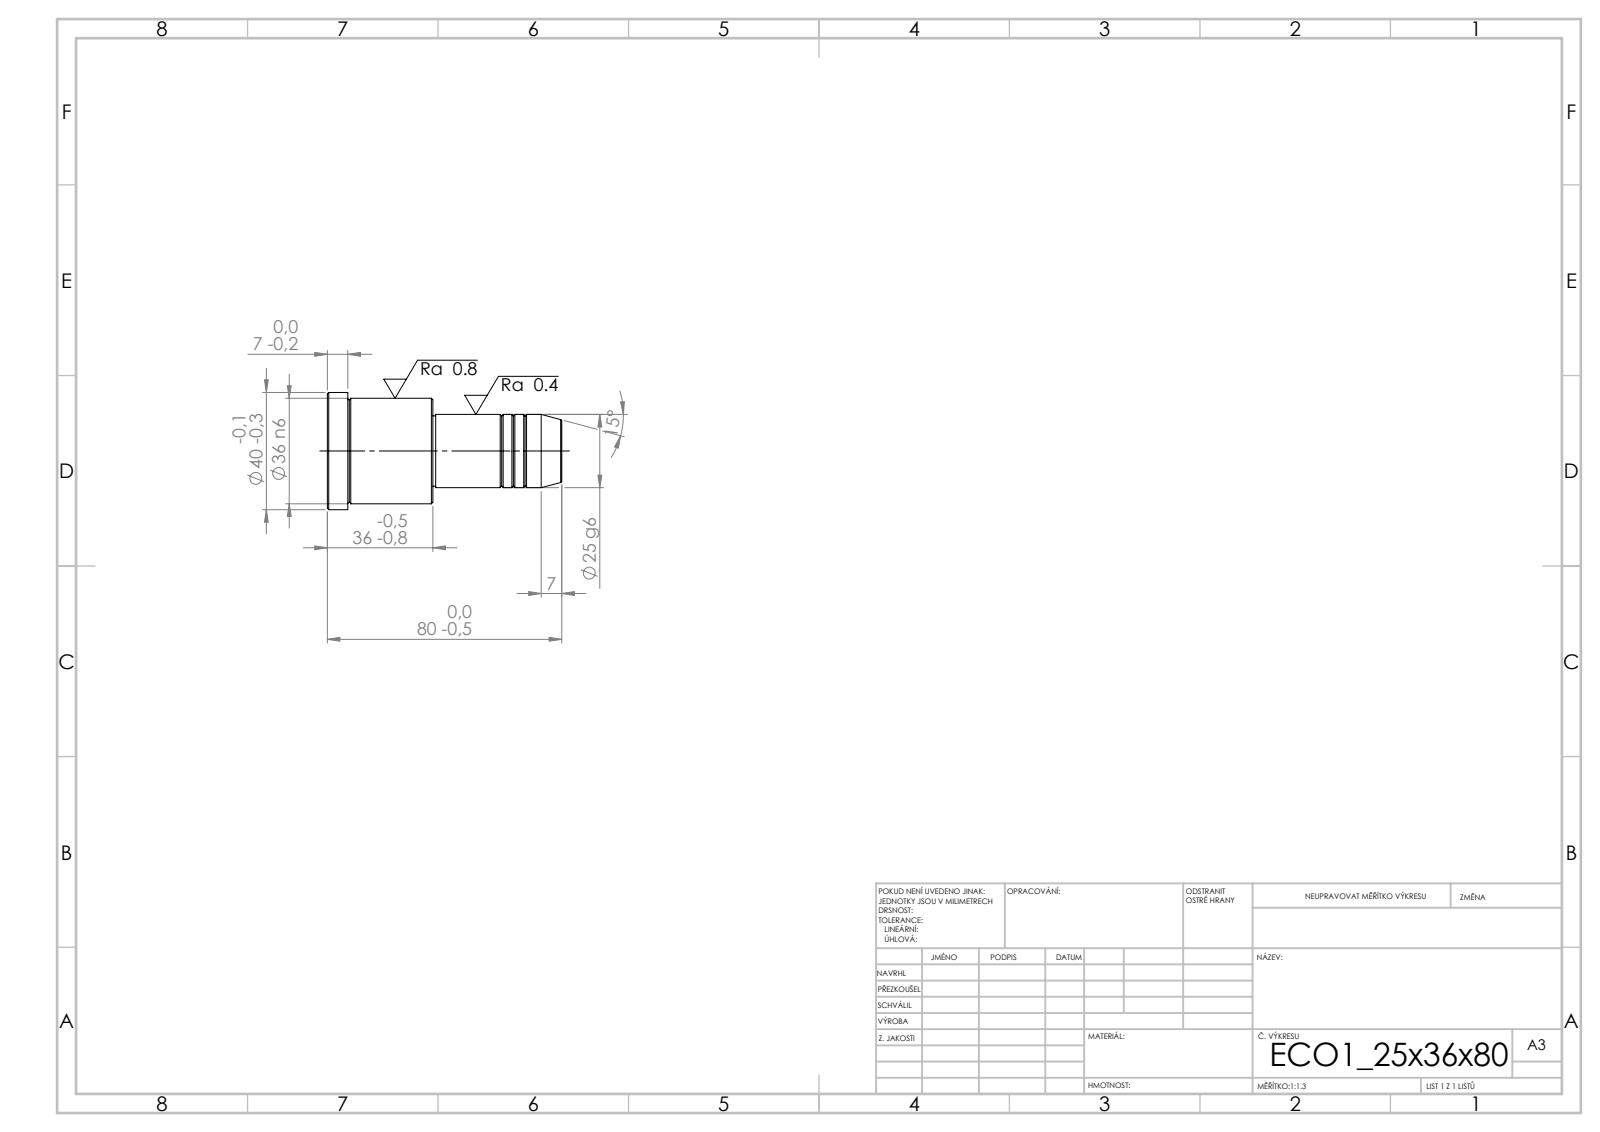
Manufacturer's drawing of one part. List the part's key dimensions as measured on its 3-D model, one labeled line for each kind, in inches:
STEP written by: SolidWorks 2019 (CONFIG_CONTROL_DESIGN)
Units: inches
Bodies: 1 solid, 43 faces (5 planar, 14 cylindrical, 24 other)
Overall size (bounding box): 3.15 × 1.575 × 1.575
Volume: 3.614 in³ · Surface area: 15.73 in²
Round bosses / shafts (diameter × count): ⌀1.575 ×1, ⌀1.417 ×1, ⌀0.984 ×1, ⌀0.945 ×1
Main face-to-face distances: 1.417, 1.732, 3.15, 2.874, 1.142, 0.276, 1.693, 0.039, 1.181, 1.457
